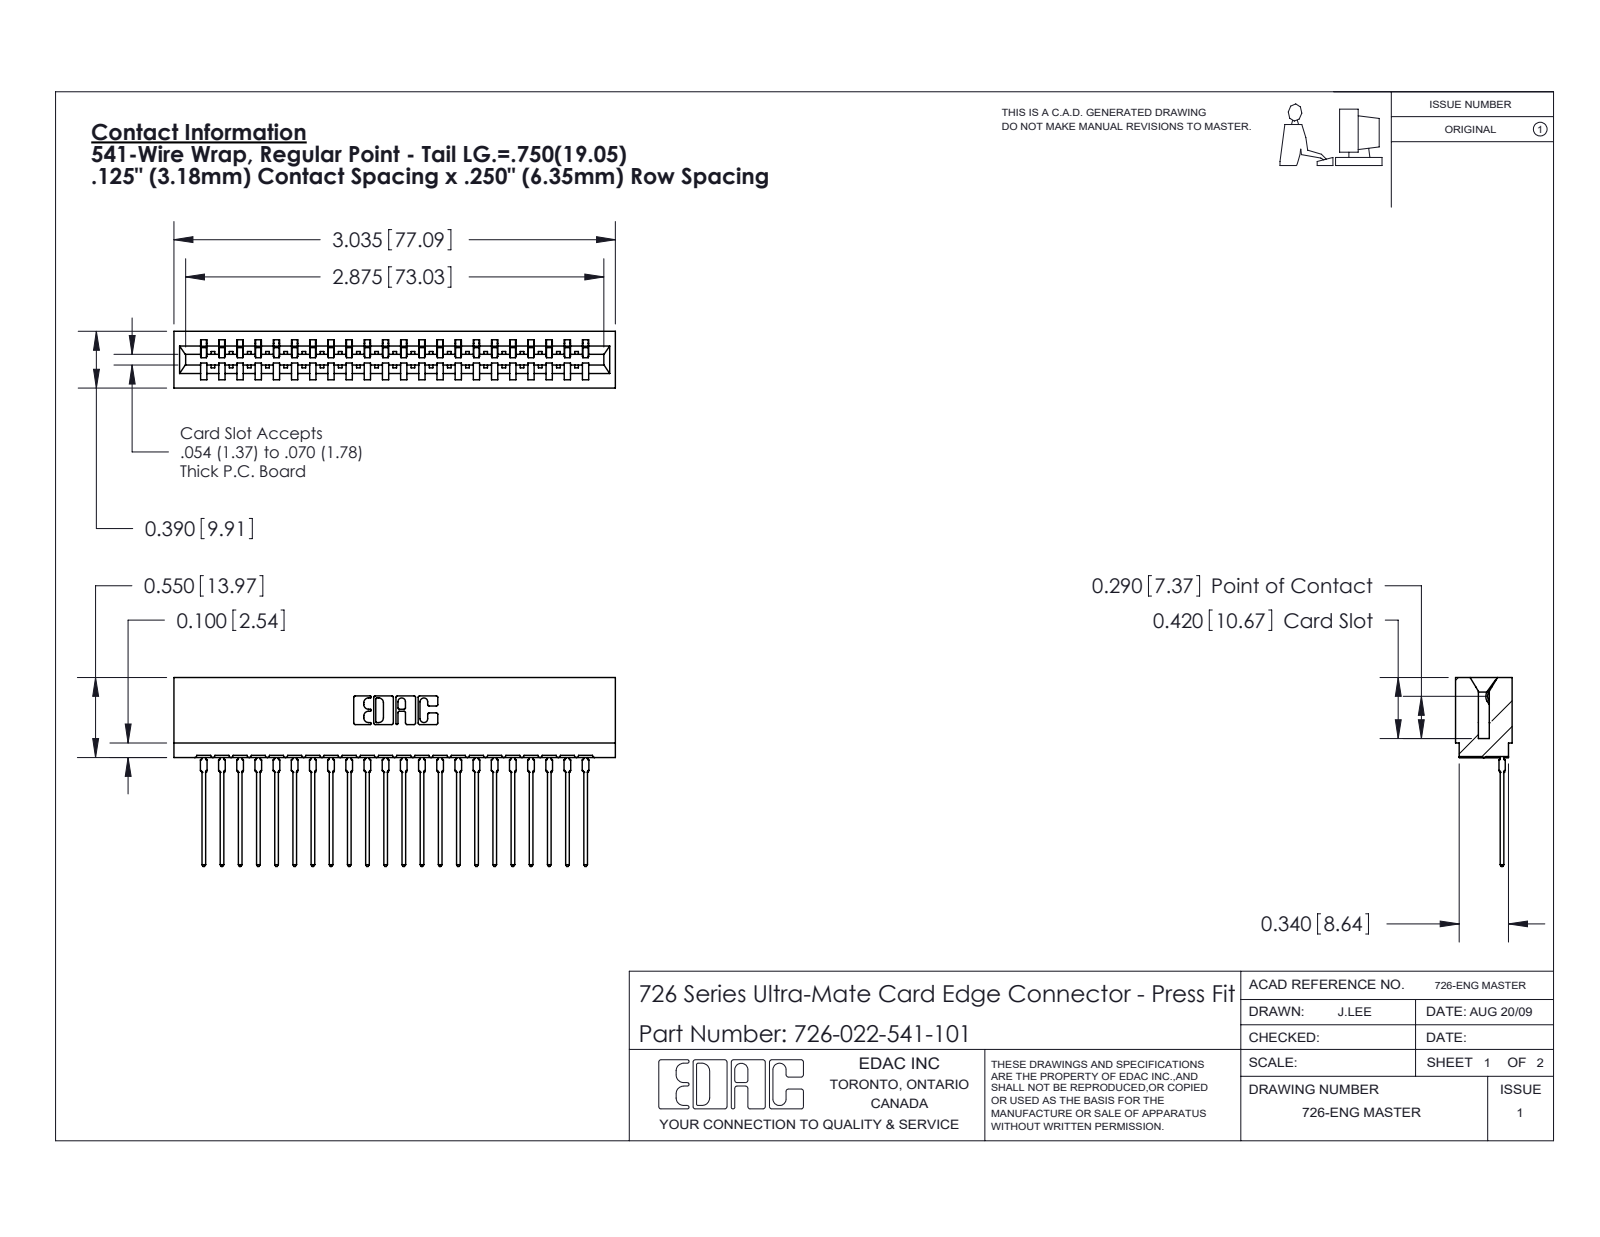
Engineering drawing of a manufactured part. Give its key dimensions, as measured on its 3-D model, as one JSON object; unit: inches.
{"part_name": "726 Part_.515 Slot Depth - 01; 746-292-001_541; 726-022-541-101", "step_written_by": "SolidWorks 2020 (CONFIG_CONTROL_DESIGN)", "units": "inches", "bodies": {"solids": 23, "faces": 2473, "planar": 1441, "cylindrical": 460, "other": 572}, "overall_size": [3.035, 1.299, 0.39], "volume_in3": 0.433, "surface_area_in2": 17.16, "partial_cylinders_radius": [[0.021, 44], [0.015, 23], [0.01, 22], [0.007, 6], [0.031, 6], [0.005, 4], [0.011, 4], [0.026, 3]], "face_to_face_distances": [0.057, 0.333, 0.39, 0.025, 0.307, 0.25, 0.083, 0.042, 1.25, 0.125]}
